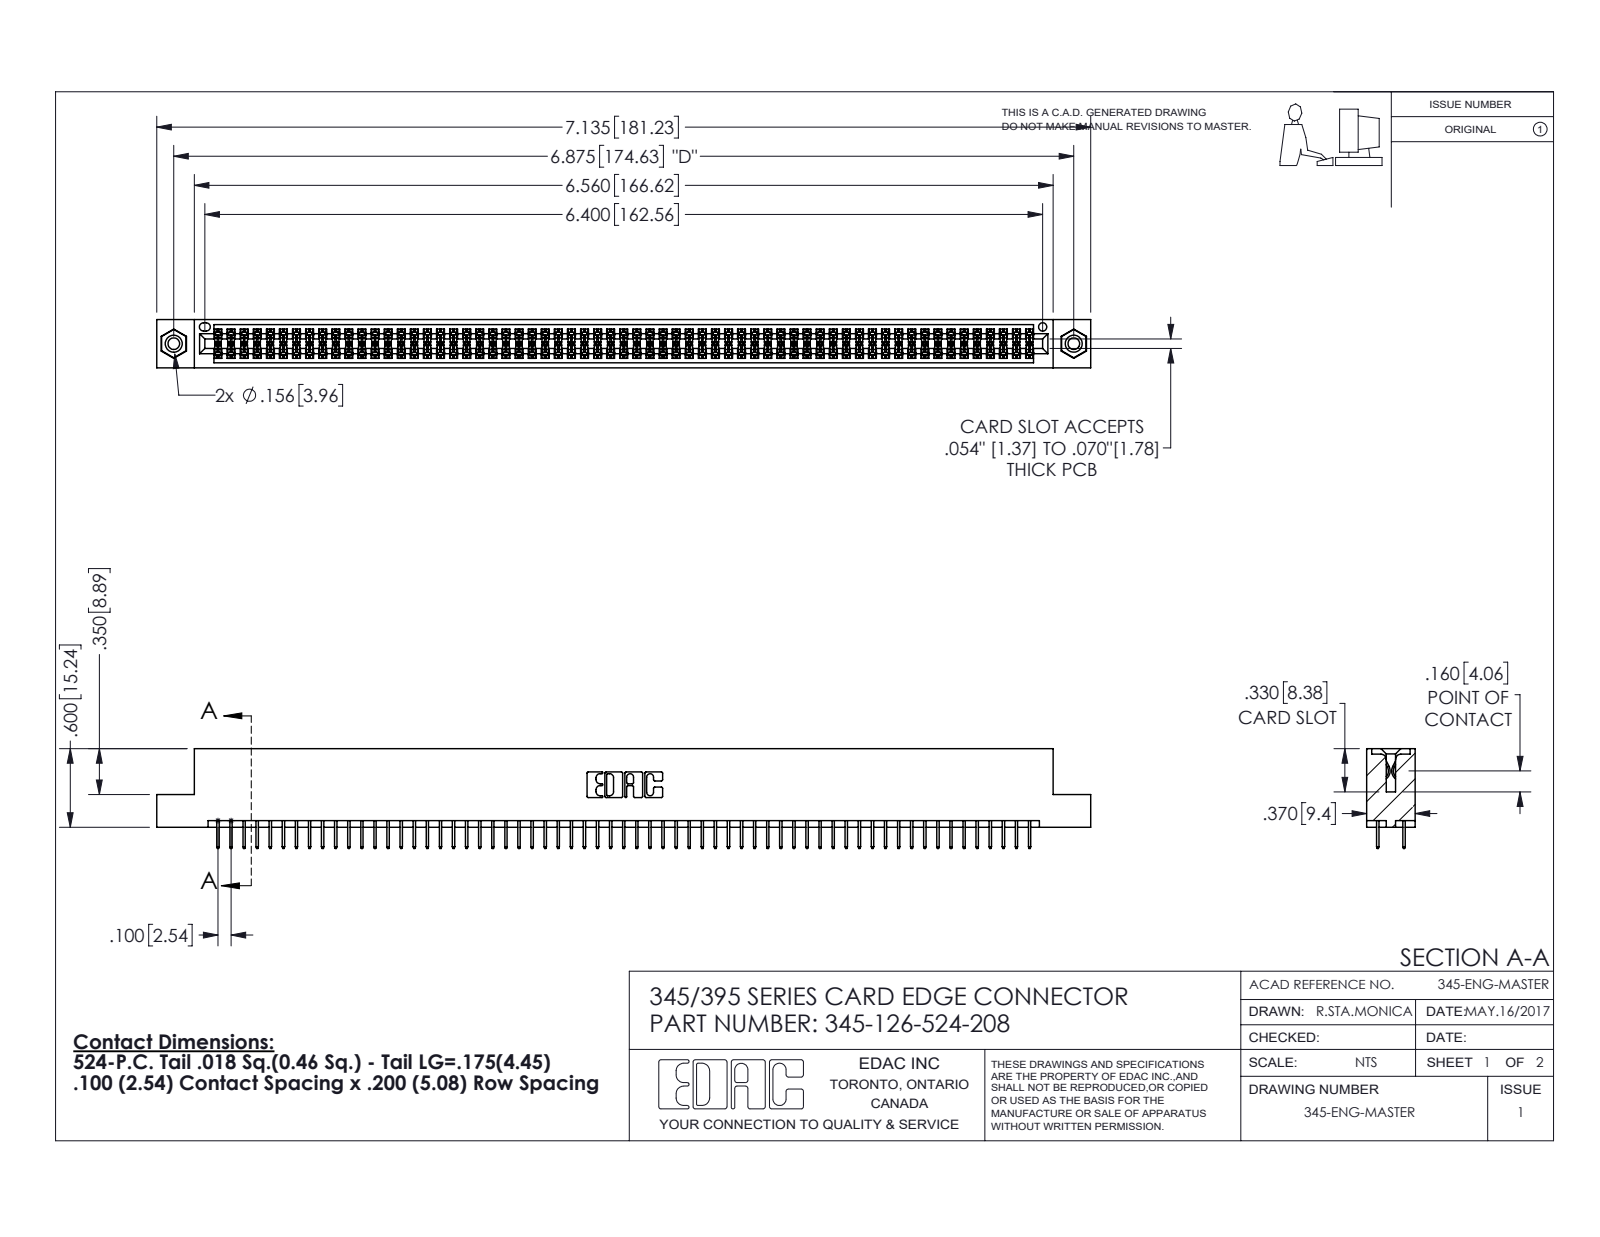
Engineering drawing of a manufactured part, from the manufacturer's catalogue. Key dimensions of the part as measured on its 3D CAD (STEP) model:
Part name (STEP PRODUCT): 345-126-524-208; 345-292-001_345-293-124; 345-250-001_345-250-003-102; 345 Part_Flush Mounting Lugs - 0.156 Dia-TI
STEP written by: SolidWorks 2016 (CONFIG_CONTROL_DESIGN)
Units: inches
Bodies: 129 solids, 6990 faces (5026 planar, 1948 cylindrical, 16 other)
Overall size (bounding box): 7.135 × 0.762 × 0.37
Volume: 1.074 in³ · Surface area: 40.2 in²
Round holes (diameter × count): ⌀0.089 ×2, ⌀0.125 ×2, ⌀0.156 ×2, ⌀0.064 ×1
Round bosses / shafts (diameter × count): ⌀0.155 ×2
Partial cylindrical surfaces — rounded edges, fillets, slot ends (radius × count): R0.006 ×189, R0.01 ×22, R0.007 ×6, R0.031 ×6, R0.026 ×3, R0.014 ×2, R0.019 ×2, R0.022 ×2
Main face-to-face distances: 0.072, 0.298, 0.2, 0.37, 0.098, 0.272, 0.025, 0.225, 0.072, 0.175
Hole centre spacings: 0.27, 6.639, 6.875
